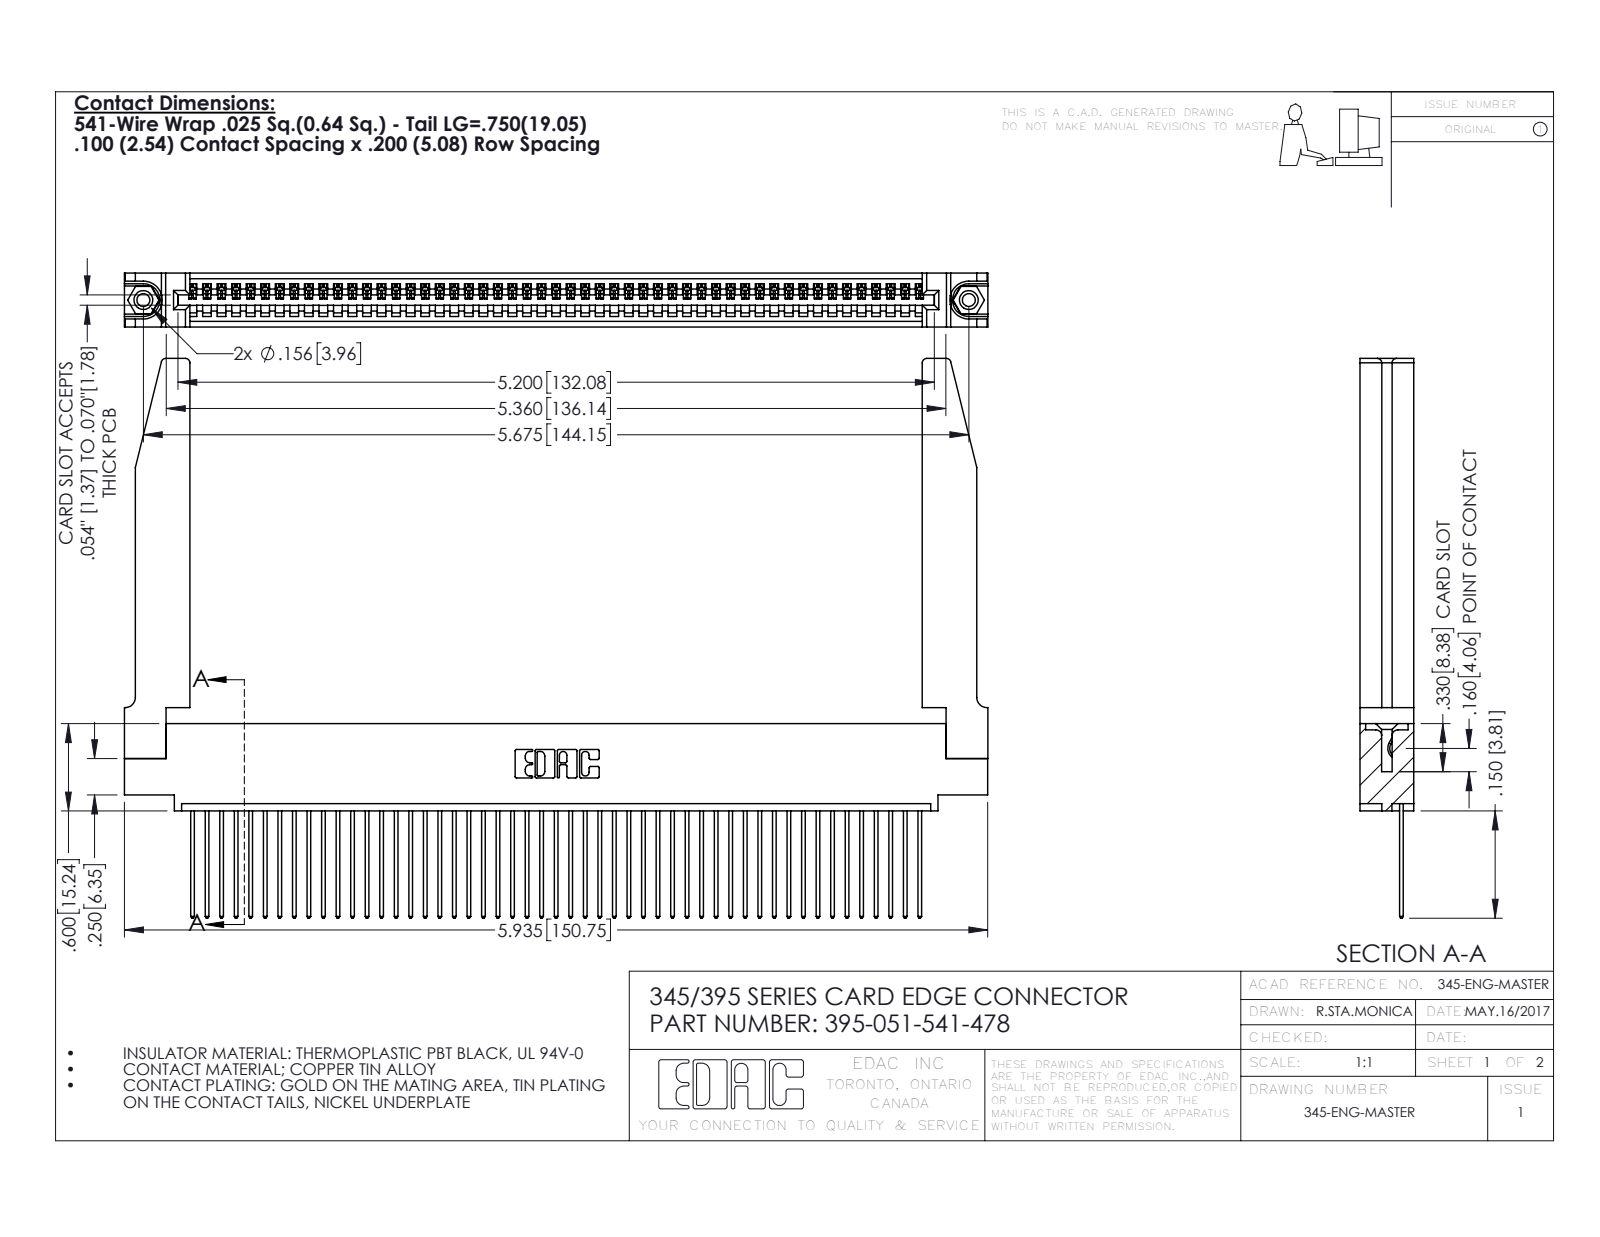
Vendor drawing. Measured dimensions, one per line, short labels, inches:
name: 345-220-078_345-220-078; 345 Part_0.110 Offset - 0.156 Dia-TH; 345-292-001_345-293-141; 395-051-541-478 (+1 more)
written by: SolidWorks 2016 (CONFIG_CONTROL_DESIGN)
unit: in
bodies: 56 solids, 3322 faces (2266 planar, 1004 cylindrical, 52 other)
size: 5.936 × 3.847 × 0.37
volume: 1.358 in³; area: 42.31 in²
holes: 2× ⌀0.089, 2× ⌀0.125, 2× ⌀0.156, 1× ⌀0.064
bosses: 2× ⌀0.155
rounds: 102× R0.006, 102× R0.01, 22× R0.01, 8× R0.03, 6× R0.007, 6× R0.031, 3× R0.026, 2× R0.031
face distances: 0.072, 0.298, 0.37, 0.098, 0.272, 0.025, 0.2, 0.225, 0.148, 0.15
hole spacings: 0.27, 5.439, 5.675
